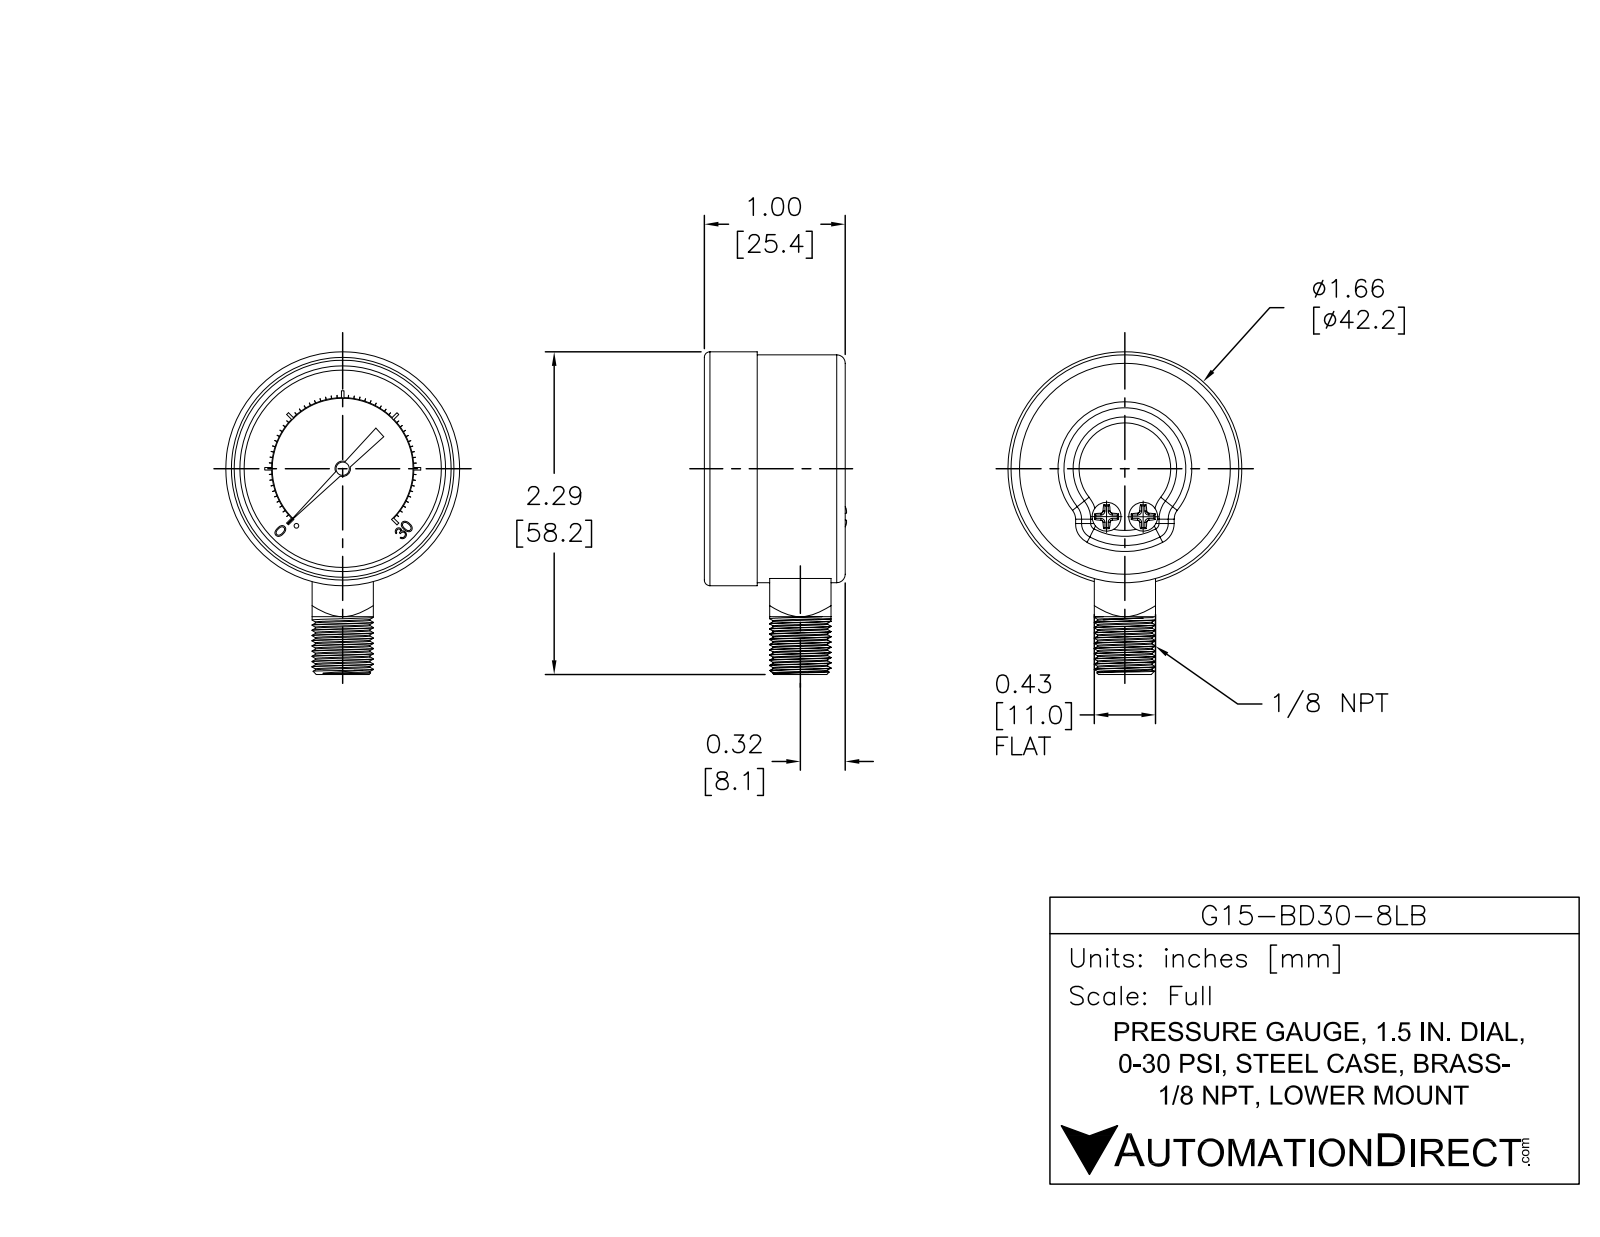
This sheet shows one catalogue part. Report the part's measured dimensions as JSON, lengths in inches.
{"part_name": "G15-BD30-8LB", "step_written_by": "SolidWorks 2021 (AUTOMOTIVE_DESIGN)", "units": "inches", "bodies": {"solids": 1, "faces": 417, "planar": 265, "cylindrical": 82, "other": 70}, "overall_size": [2.29, 1.66, 1.01], "volume_in3": 1.682, "surface_area_in2": 12.05, "round_holes": [[0.14, 1], [1.4, 1]], "round_bosses_or_shafts": [[0.205, 2], [1.66, 1], [1.617, 1], [0.435, 1], [0.11, 1], [0.095, 1], [0.033, 1]], "partial_cylinders_radius": [[0.06, 4], [0.5, 1], [0.505, 1]], "face_to_face_distances": [0.71, 0.1, 0.61, 0.435, 0.96, 0.86, 0.25, 0.04, 0.625, 0.525]}
